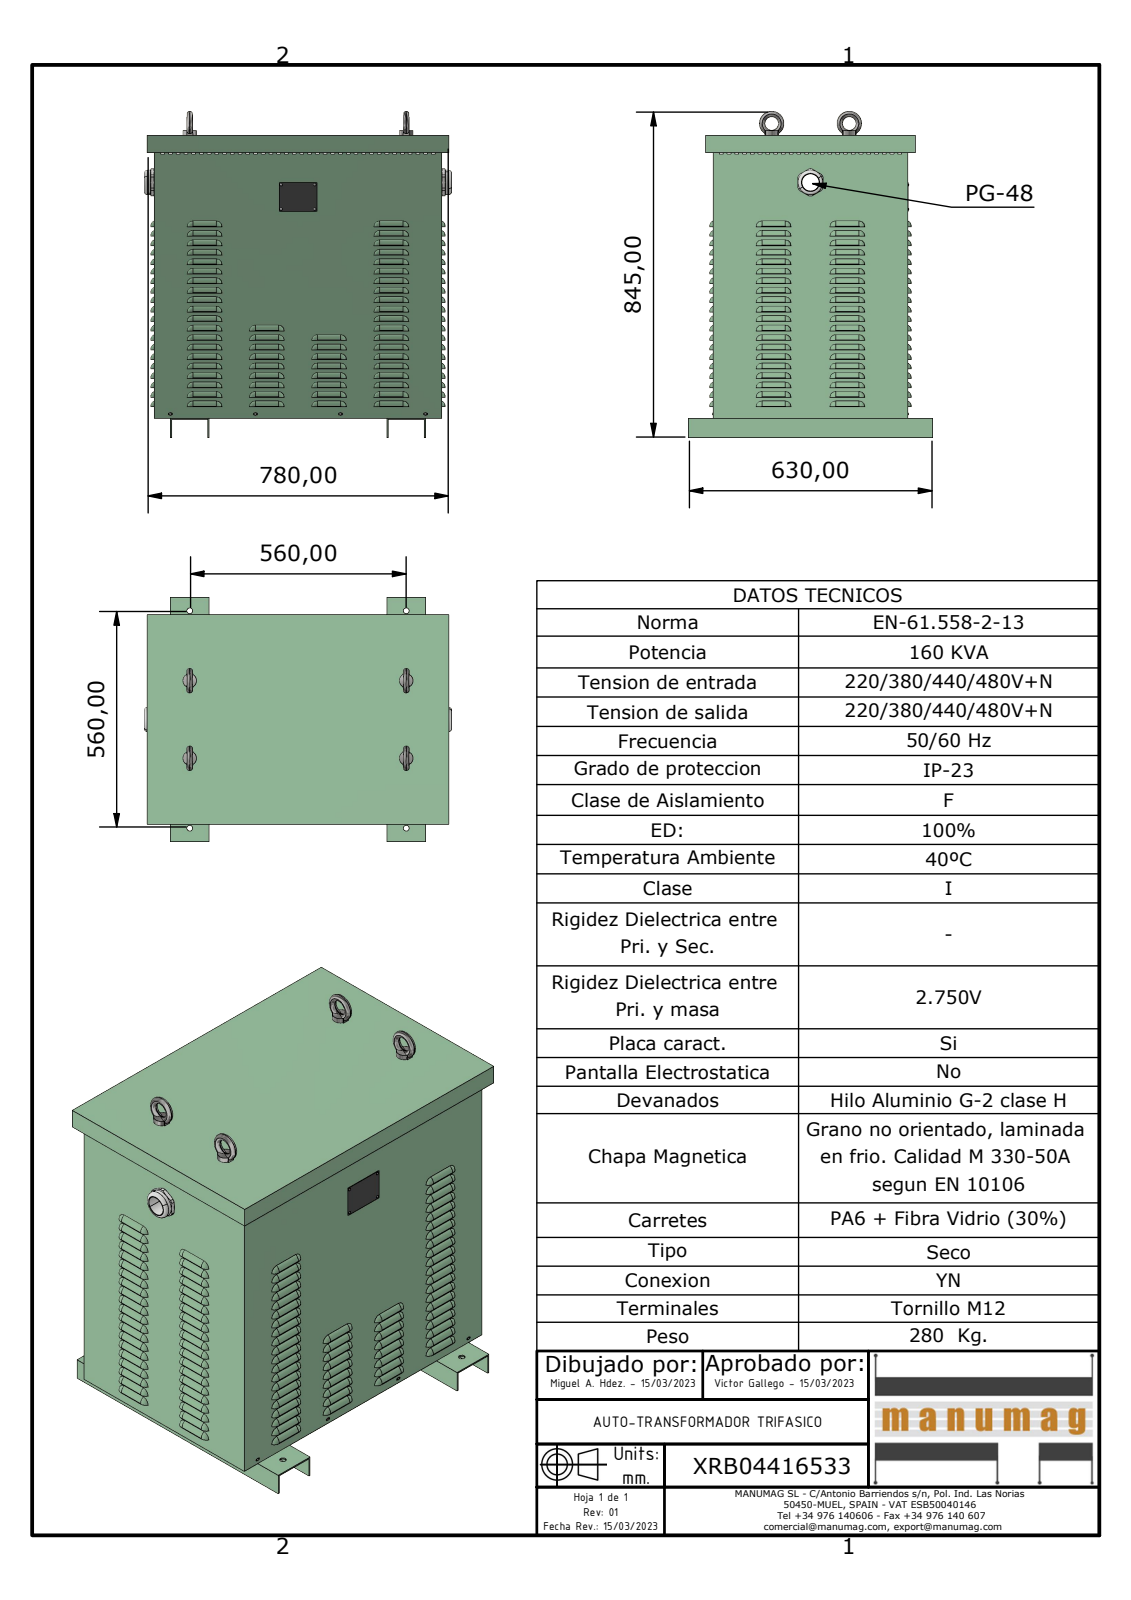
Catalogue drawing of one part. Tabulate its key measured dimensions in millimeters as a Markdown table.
| quantity | value |
| --- | --- |
| part name | XRB04416533; JE160 EXPORT JE200 EXPORT NACIONAL BASE; JE160 EXPORT JE200 EXPORT NACIONAL PATA; JE160 EXPORT CUERPO (+5 more) |
| STEP written by | Autodesk Inventor 2023 (AUTOMOTIVE_DESIGN) |
| units | millimeters |
| bodies | 24 solids, 4187 faces (1441 planar, 1866 cylindrical, 880 other) |
| overall size | 844 × 795.27 × 630 |
| volume | 7 086 000 mm³ |
| surface area | 6 256 000 mm² |
| round holes (diameter × count) | 11 × 936, 15 × 8, 4 × 4, 5 × 4, 35 × 2, 44 × 1, 60 × 1 |
| round bosses / shafts (diameter × count) | 3.2 × 8, 16 × 4, 14.8 × 4, 63 × 3, 59.3 × 1, 59.15 × 1, 57.63 × 1 |
| partial cylindrical surfaces (radius × count) | 14 × 194, 7 × 84, 15 × 80, 2.5 × 8, 2 × 4, 17.5 × 4, 35 × 1 |
| main face-to-face distances | 2, 500, 730, 742, 498, 502, 732, 740, 728, 744 |
| hole center spacings | 15, 30, 33.54, 204.55, 159.71, 204, 129.87, 159 |
